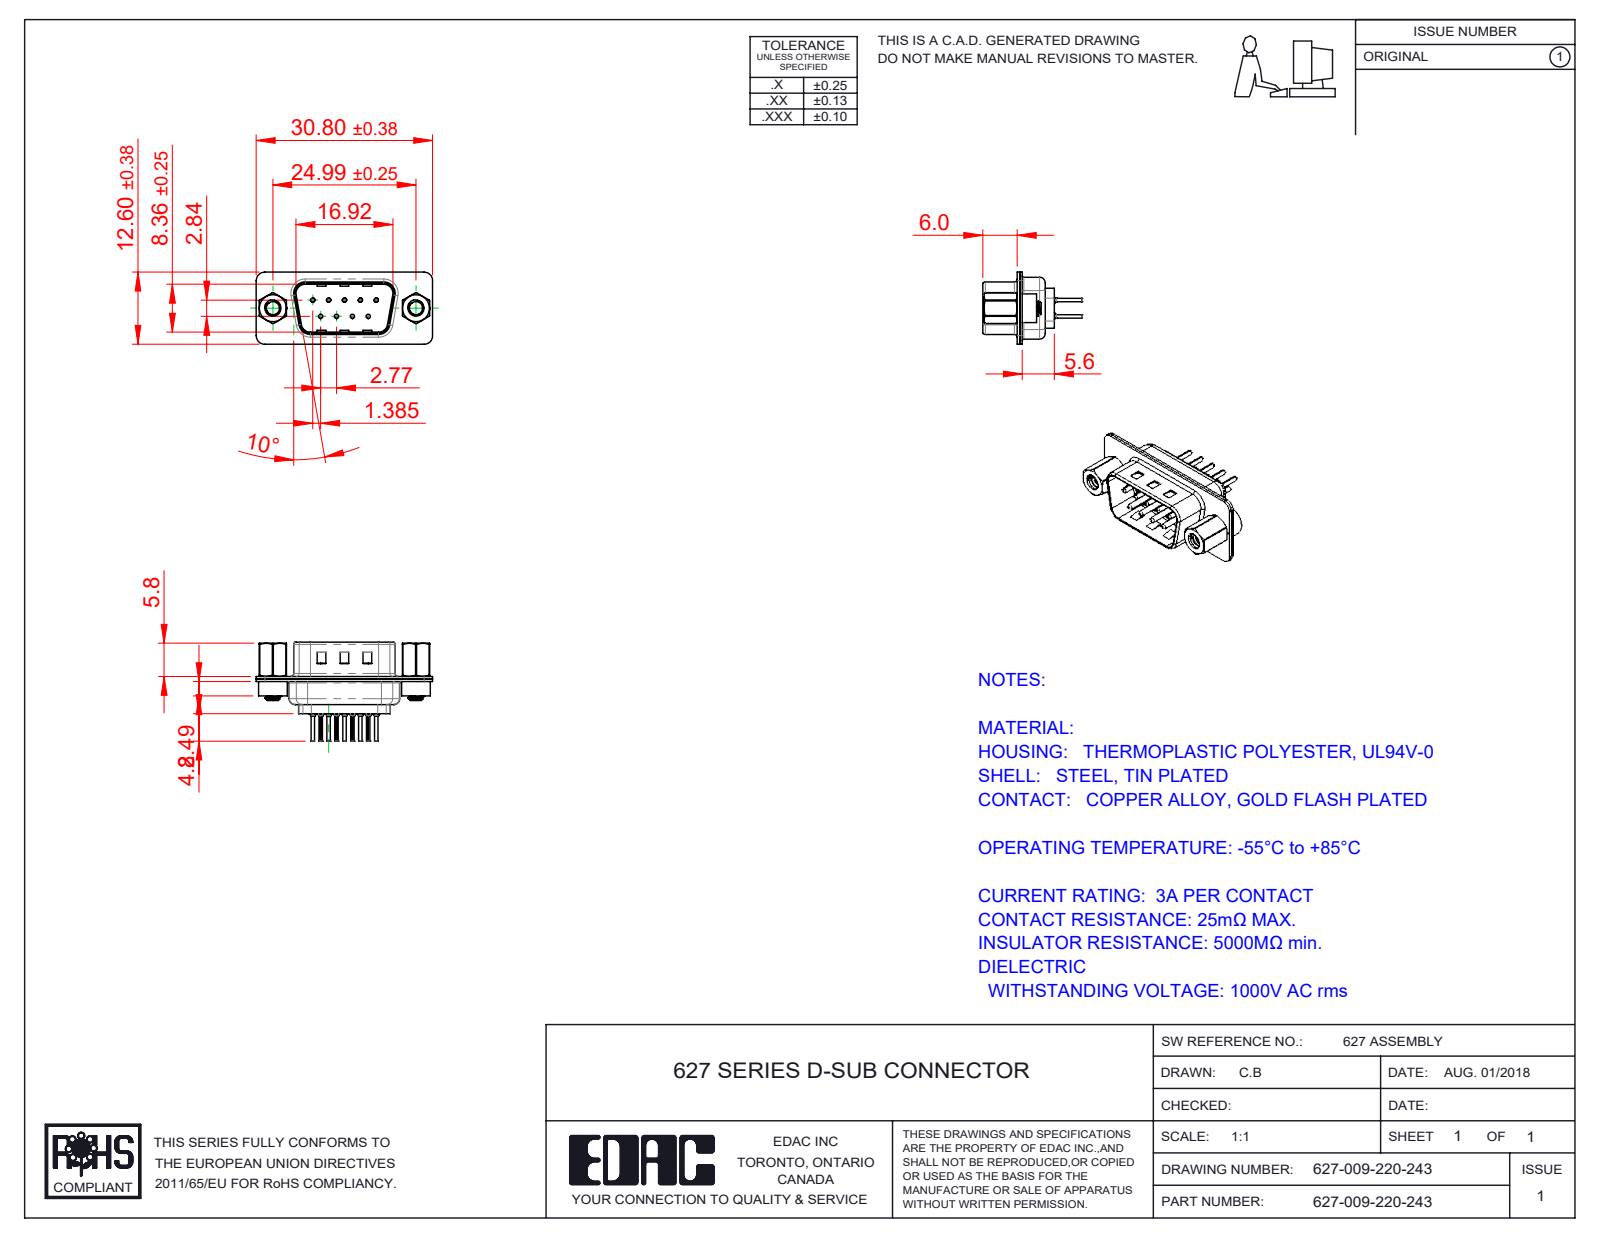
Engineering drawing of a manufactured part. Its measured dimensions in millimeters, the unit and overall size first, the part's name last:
Units: millimetres
Overall size (bounding box): 30.8 × 17.3 × 12.6
Round holes (diameter × count): ⌀0.2 ×9, ⌀0.35 ×9, ⌀1.1 ×9, ⌀1.6 ×9, ⌀2.26 ×2, ⌀2.29 ×2, ⌀4 ×2, ⌀4.8 ×2
Round bosses / shafts (diameter × count): ⌀2 ×9, ⌀1.5 ×9, ⌀0.75 ×9, ⌀0.6 ×9, ⌀5 ×2, ⌀4.9 ×2, ⌀2.79 ×2
Partial cylindrical surfaces — rounded edges, fillets, slot ends (radius × count): R0.1 ×18, R1.5 ×18, R2 ×12, R0.5 ×8, R1.6 ×8, R0.25 ×4, R0.6 ×4, R0.65 ×4
Main face-to-face distances: 0.45, 0.4, 0.9, 0.82, 9.58, 1.4, 8.76, 0.5, 1.5, 5.6
Hole centre spacings: 3.16, 2.77, 5.54, 5.03, 5.04, 8.31, 7.48, 7.49
Volume: 1 519 mm³ · Surface area: 4 406 mm²
Bodies: 16 solids, 1308 faces (345 planar, 532 cylindrical, 431 other)
Part name (STEP PRODUCT): 627 Housing_09 LP; 627 Contact Row 1_20L; 627 Contact Row 2_20L; 627 Shell Front_09 Contacts (+4 more)
STEP written by: SolidWorks 2020 (CONFIG_CONTROL_DESIGN)
